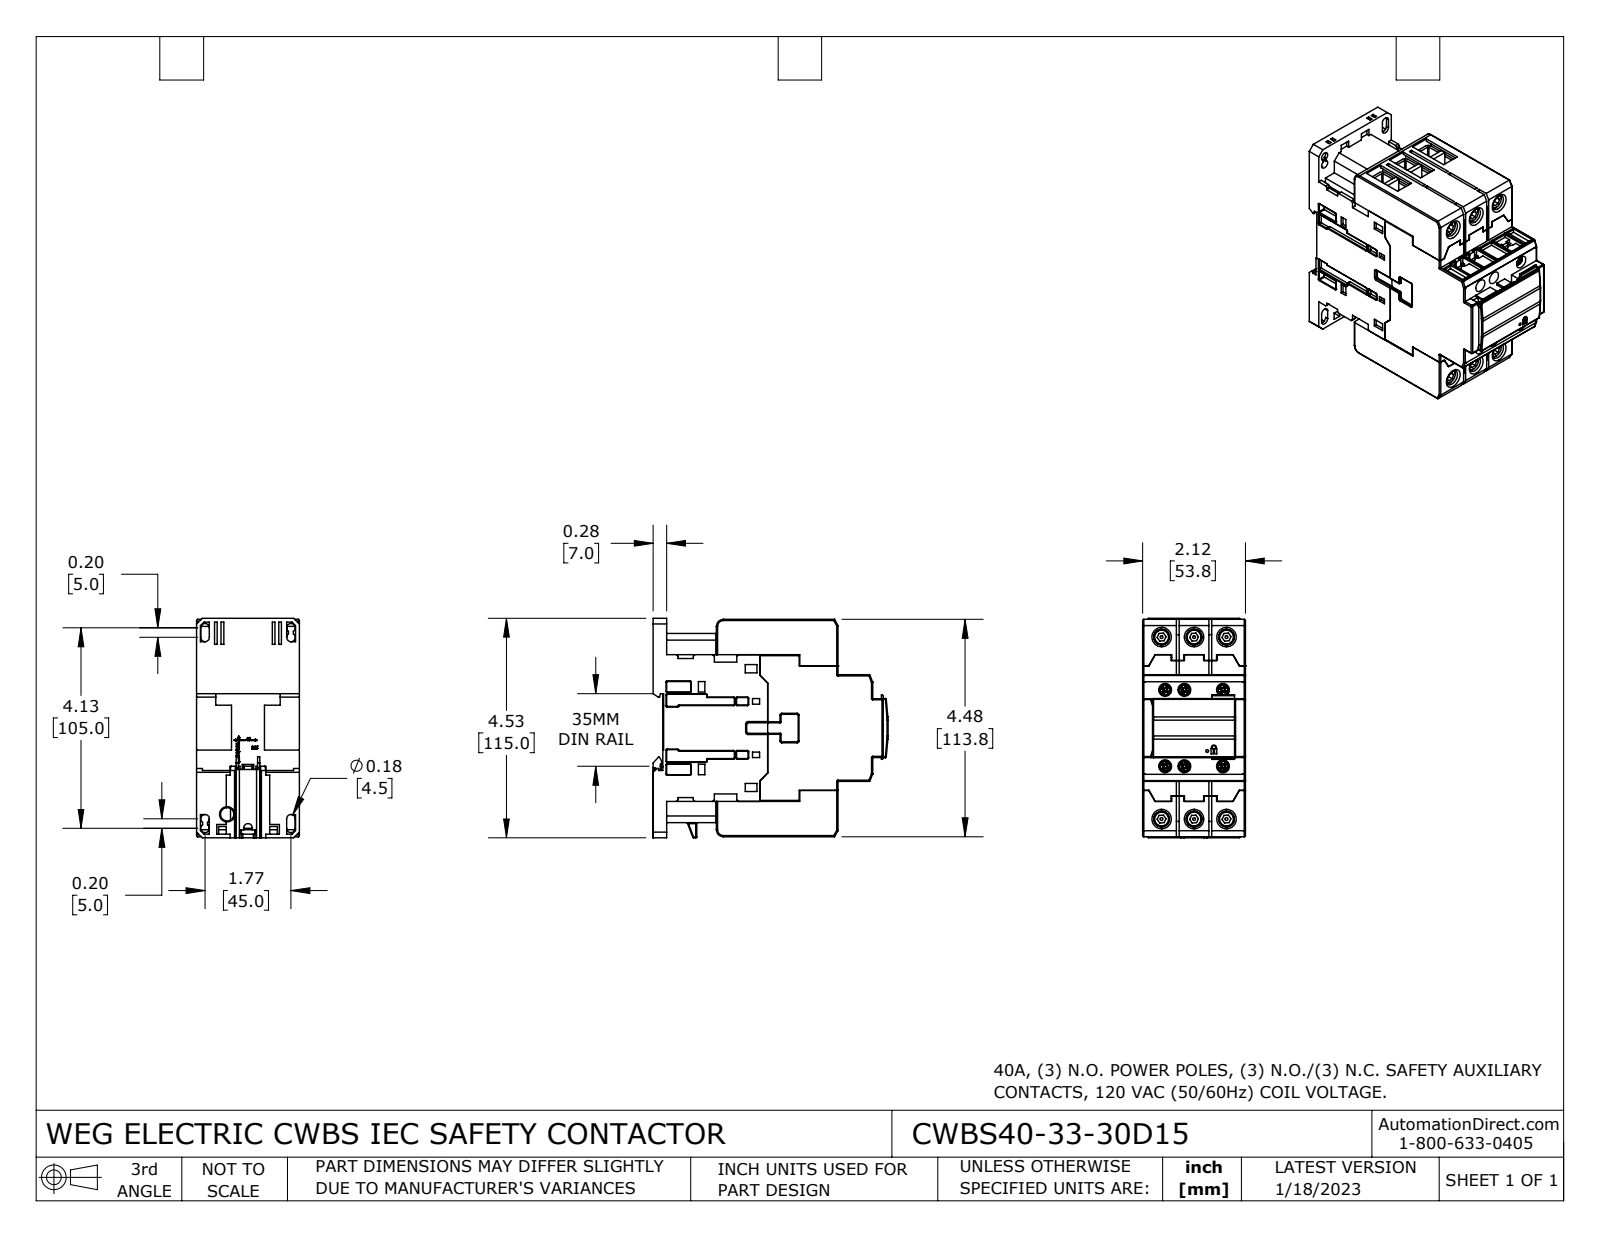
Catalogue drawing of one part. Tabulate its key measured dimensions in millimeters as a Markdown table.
| quantity | value |
| --- | --- |
| part name | CWBS40-33-30D15 |
| STEP written by | SolidWorks 2021 (CONFIG_CONTROL_DESIGN) |
| units | millimeters |
| bodies | 37 solids, 2637 faces (1669 planar, 550 cylindrical, 418 other) |
| overall size | 123.1 × 115 × 53.8 |
| volume | 551 800 mm³ |
| surface area | 135 000 mm² |
| round holes (diameter × count) | 3.1 × 6, 5 × 6, 6.7 × 6, 8.2 × 6, 4.5 × 4, 3.2 × 2, 7 × 2, 1.5 × 1 |
| round bosses / shafts (diameter × count) | 8.7 × 6, 6 × 6, 3.4 × 6 |
| partial cylindrical surfaces (radius × count) | 0.5 × 89, 0.3 × 69, 0.1 × 48, 0.6 × 42, 2 × 18, 2.3 × 5, 1 × 3, 1.5 × 3 |
| main face-to-face distances | 1.5, 53.8, 17, 18.5, 76.8, 95.3, 2.7, 5.5, 96.8, 2.5 |
| hole center spacings | 17, 27.7, 31.5, 42.4, 67.7, 69.3, 74.9, 96.8 |
